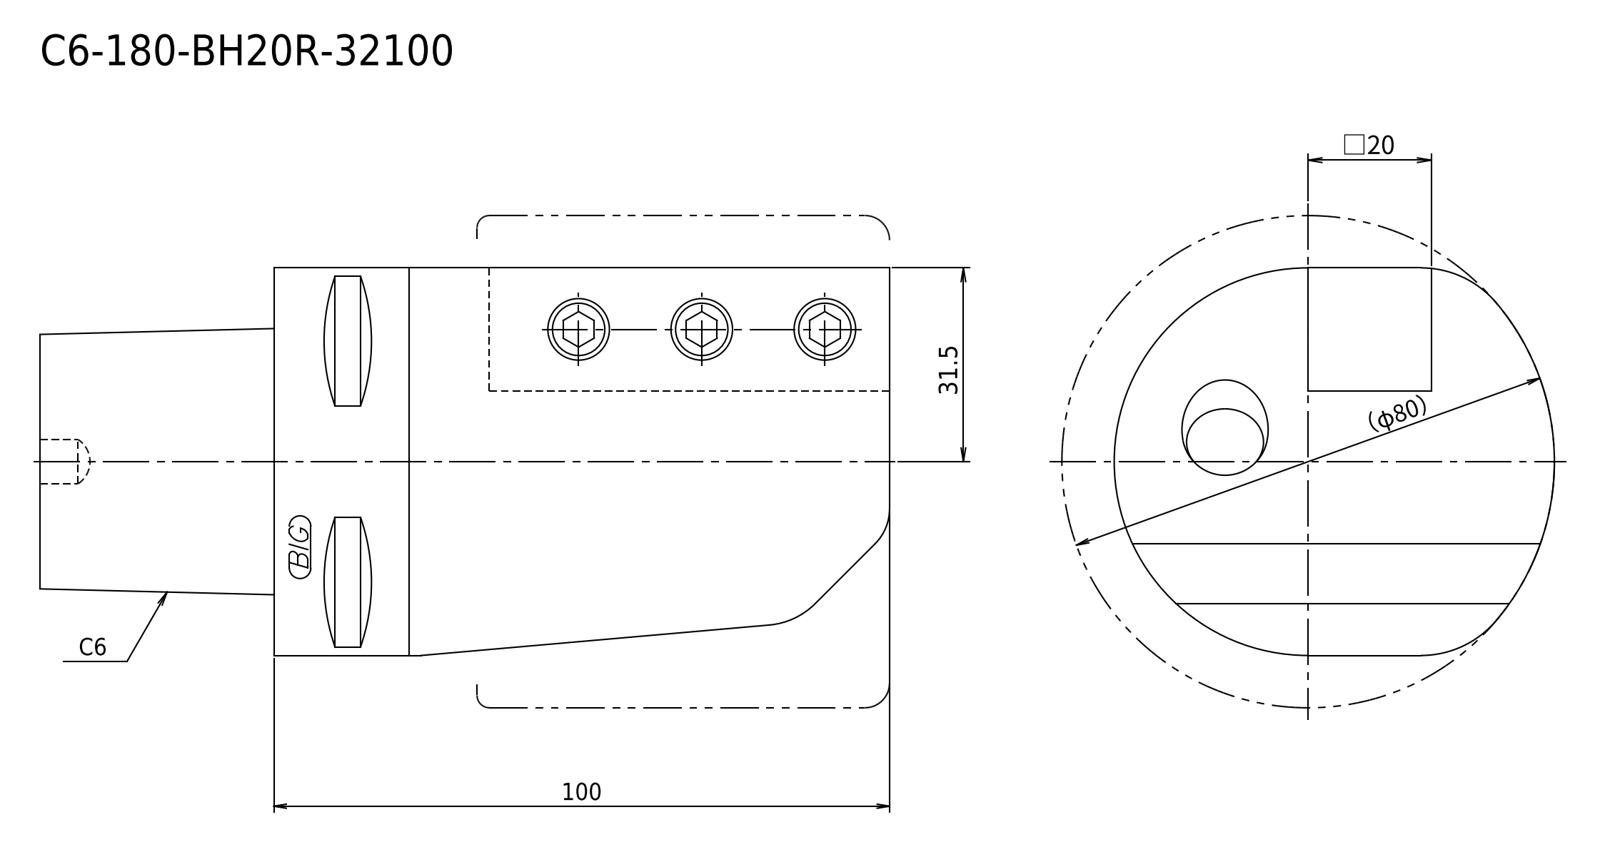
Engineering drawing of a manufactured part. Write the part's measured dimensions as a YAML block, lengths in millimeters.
part_name: "240[2]"
step_written_by: "Kubotek KeyCreator 2011 V10.0.2 (22737) (automotive_design)"
units: millimeters
bodies: {solids: 1, faces: 20, planar: 11, cylindrical: 5, other: 4}
overall_size: [138, 71.5, 62.99]
volume: 370579
surface_area: 35270
round_bosses_or_shafts:
  - {diameter: 62.98, count: 1}
partial_cylinders:
  - {radius: 16, count: 2}
  - {radius: 31.5, count: 1}
  - {radius: 40, count: 1}
face_to_face_distances: [100, 20, 138, 38, 65, 35, 73, 67, 2, 33]
